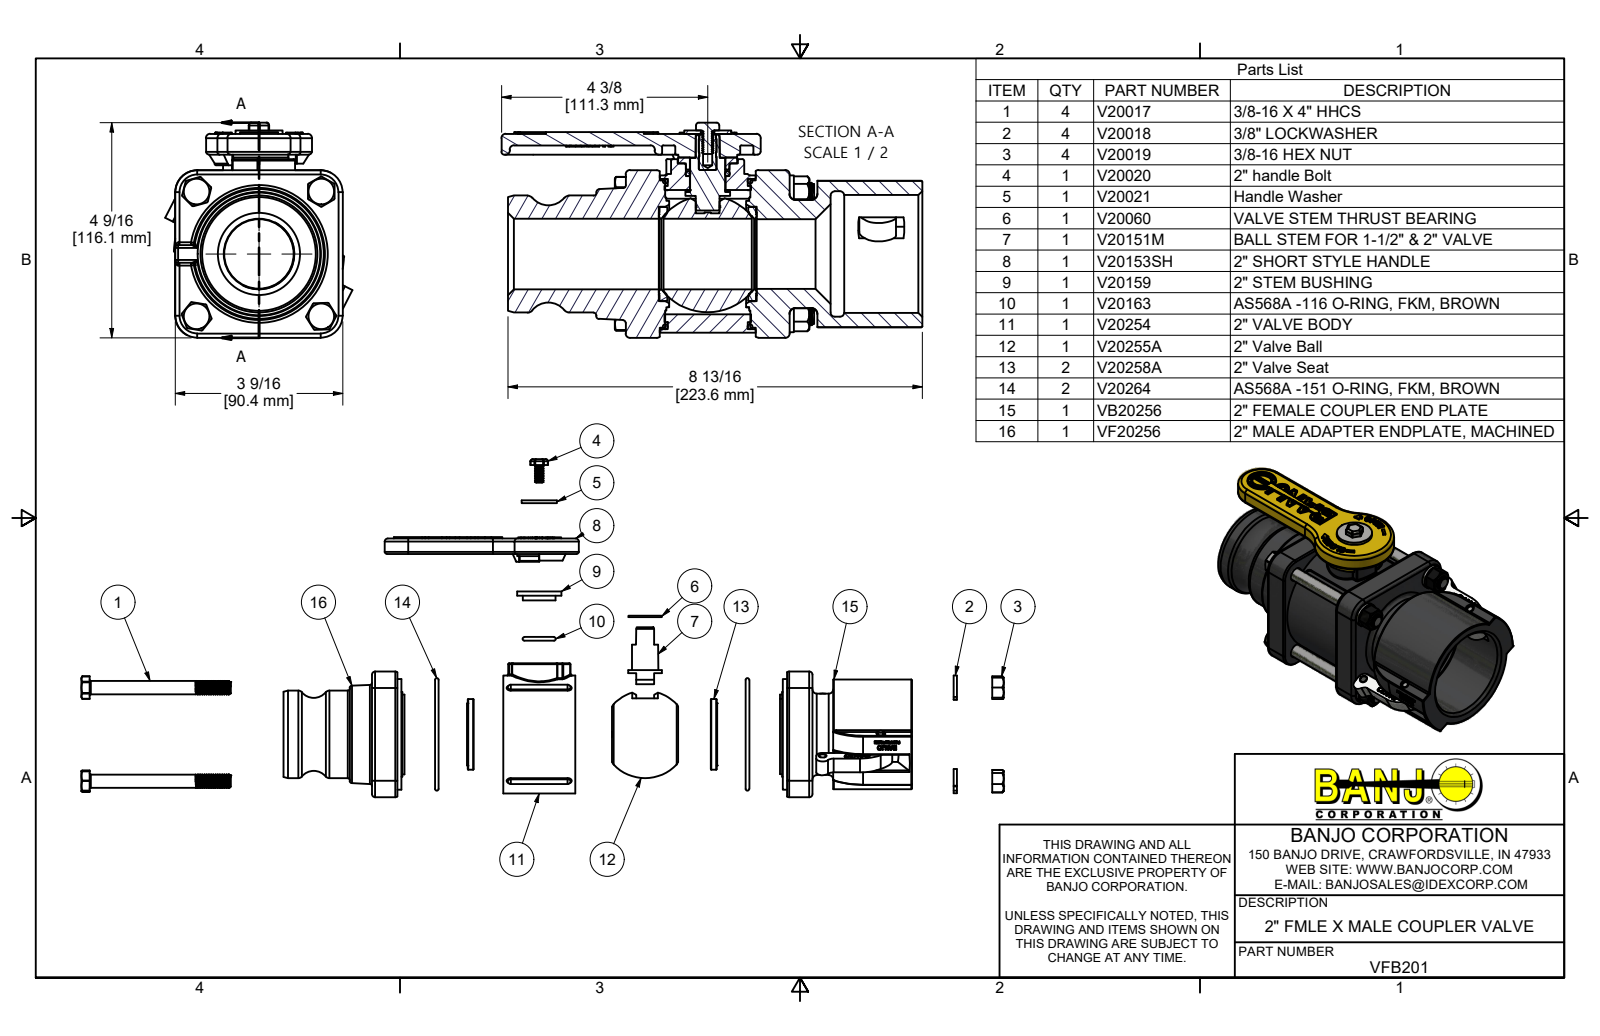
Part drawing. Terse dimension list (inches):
name: VFB201; V20254; V20017; V20018 (+8 more)
written by: Autodesk Inventor 2022 (AUTOMOTIVE_DESIGN)
unit: in
bodies: 32 solids, 2678 faces (1140 planar, 556 cylindrical, 982 other)
size: 8.94 × 4.571 × 3.978
volume: 50.22 in³; area: 347.4 in²
holes: 10× ⌀0.165, 8× ⌀0.406, 5× ⌀0.375, 4× ⌀0.307, 4× ⌀0.385, 2× ⌀0.195, 2× ⌀0.25, 2× ⌀0.258, 2× ⌀1.5, 2× ⌀1.566, 2× ⌀1.616, 1× ⌀0.196
bosses: 60× ⌀0.324, 4× ⌀0.687, 4× ⌀0.375, 2× ⌀2, 2× ⌀1.766, 2× ⌀0.26, 2× ⌀0.249, 1× ⌀3.34
rounds: 38× R0.03, 22× R0.09, 21× R0.06, 9× R0.125, 8× R0.162, 8× R0.469, 6× R0.18, 4× R0.015
face distances: 0.72, 2.76, 0.835, 2.645, 0.115, 1.925, 3.56, 2.04, 3.48, 1.81
hole spacings: 1.363, 2.316, 1.872, 2.632, 2.648, 3.128, 0.705, 0.971
